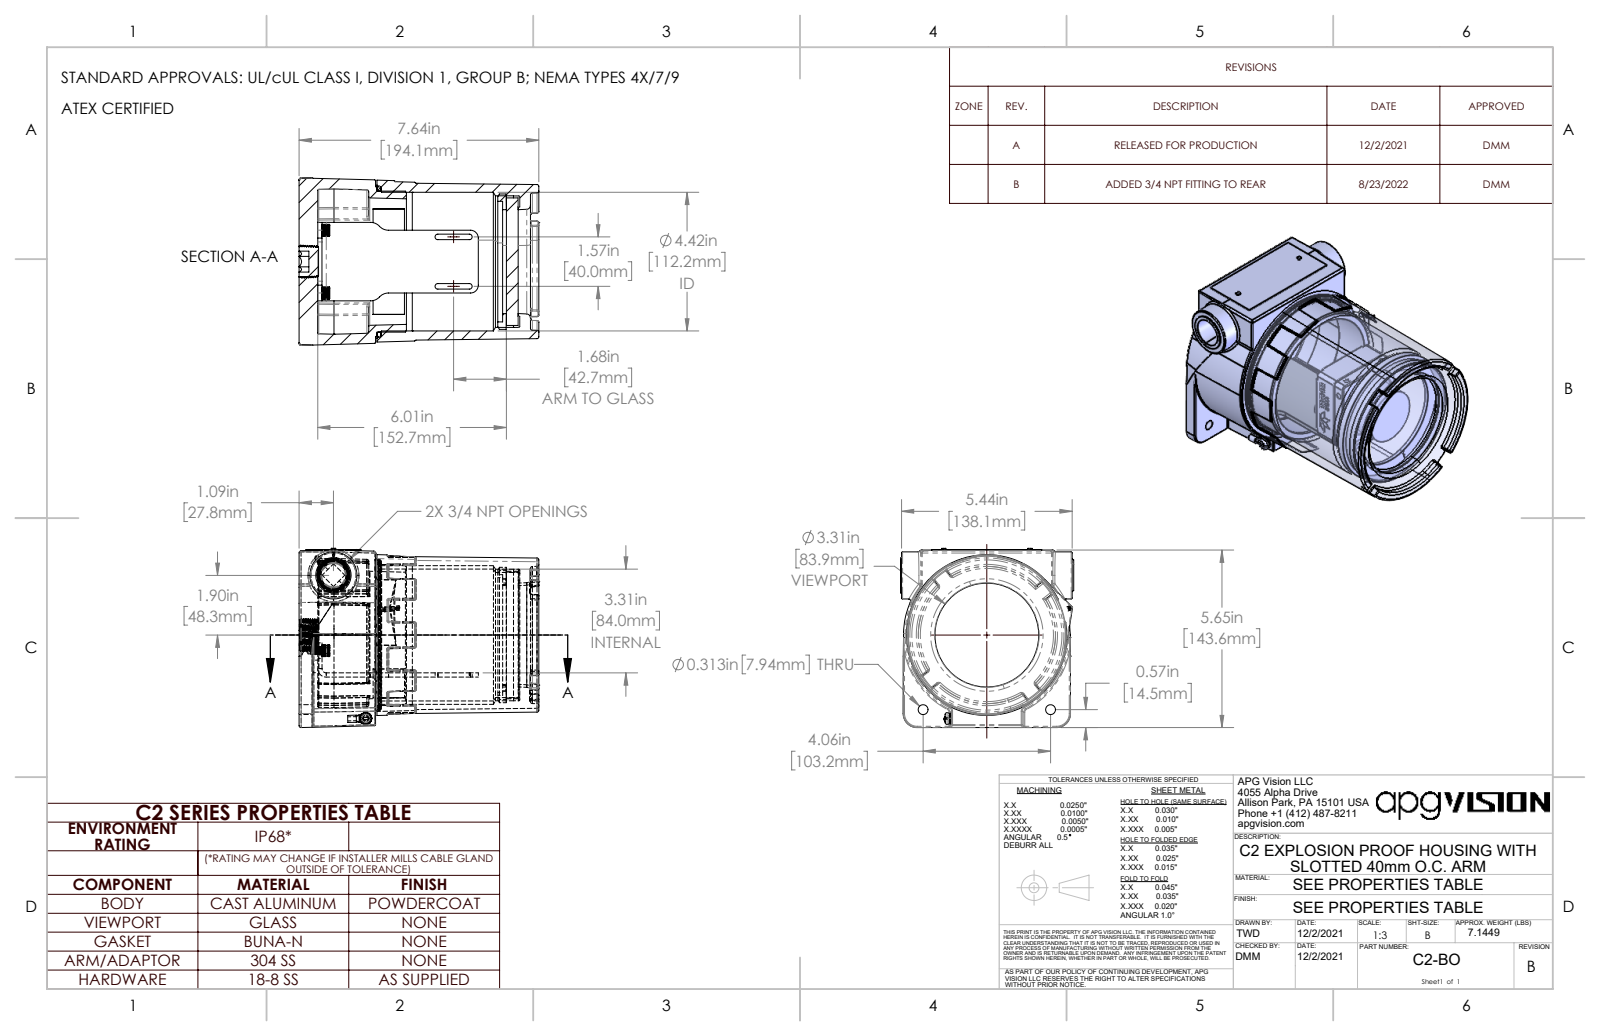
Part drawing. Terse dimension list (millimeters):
name: 200952; 92196A535_92196A535; 4638K515_4638K515; 201109 (+2 more)
written by: SolidWorks 2021 (CONFIG_CONTROL_DESIGN)
unit: mm
bodies: 22 solids, 1713 faces (471 planar, 358 cylindrical, 884 other)
size: 263.1 × 194.1 × 145
volume: 1 096 000 mm³; area: 303 400 mm²
holes: 2× ⌀1.7, 2× ⌀2.4, 2× ⌀3.7, 2× ⌀4.8, 2× ⌀5.1, 2× ⌀6.8, 2× ⌀8, 2× ⌀10.2, 1× ⌀2.7, 1× ⌀3.3, 1× ⌀5, 1× ⌀5
bosses: 2× ⌀7, 2× ⌀6.4, 2× ⌀4.8, 2× ⌀4.7, 2× ⌀4, 2× ⌀3.1, 2× ⌀1.9, 1× ⌀121.2
rounds: 19× R0.8, 11× R0.8, 5× R1.6, 5× R1.6, 4× R2.3, 4× R6.4, 4× R10, 3× R0.6
face distances: 15.1, 177.3, 162.3, 167.8, 152.7, 9.5, 3.4, 0.5, 103.3, 99.9
hole spacings: 28.4, 18, 40.2, 45.2, 52.3, 54.4, 73.2, 79.4
